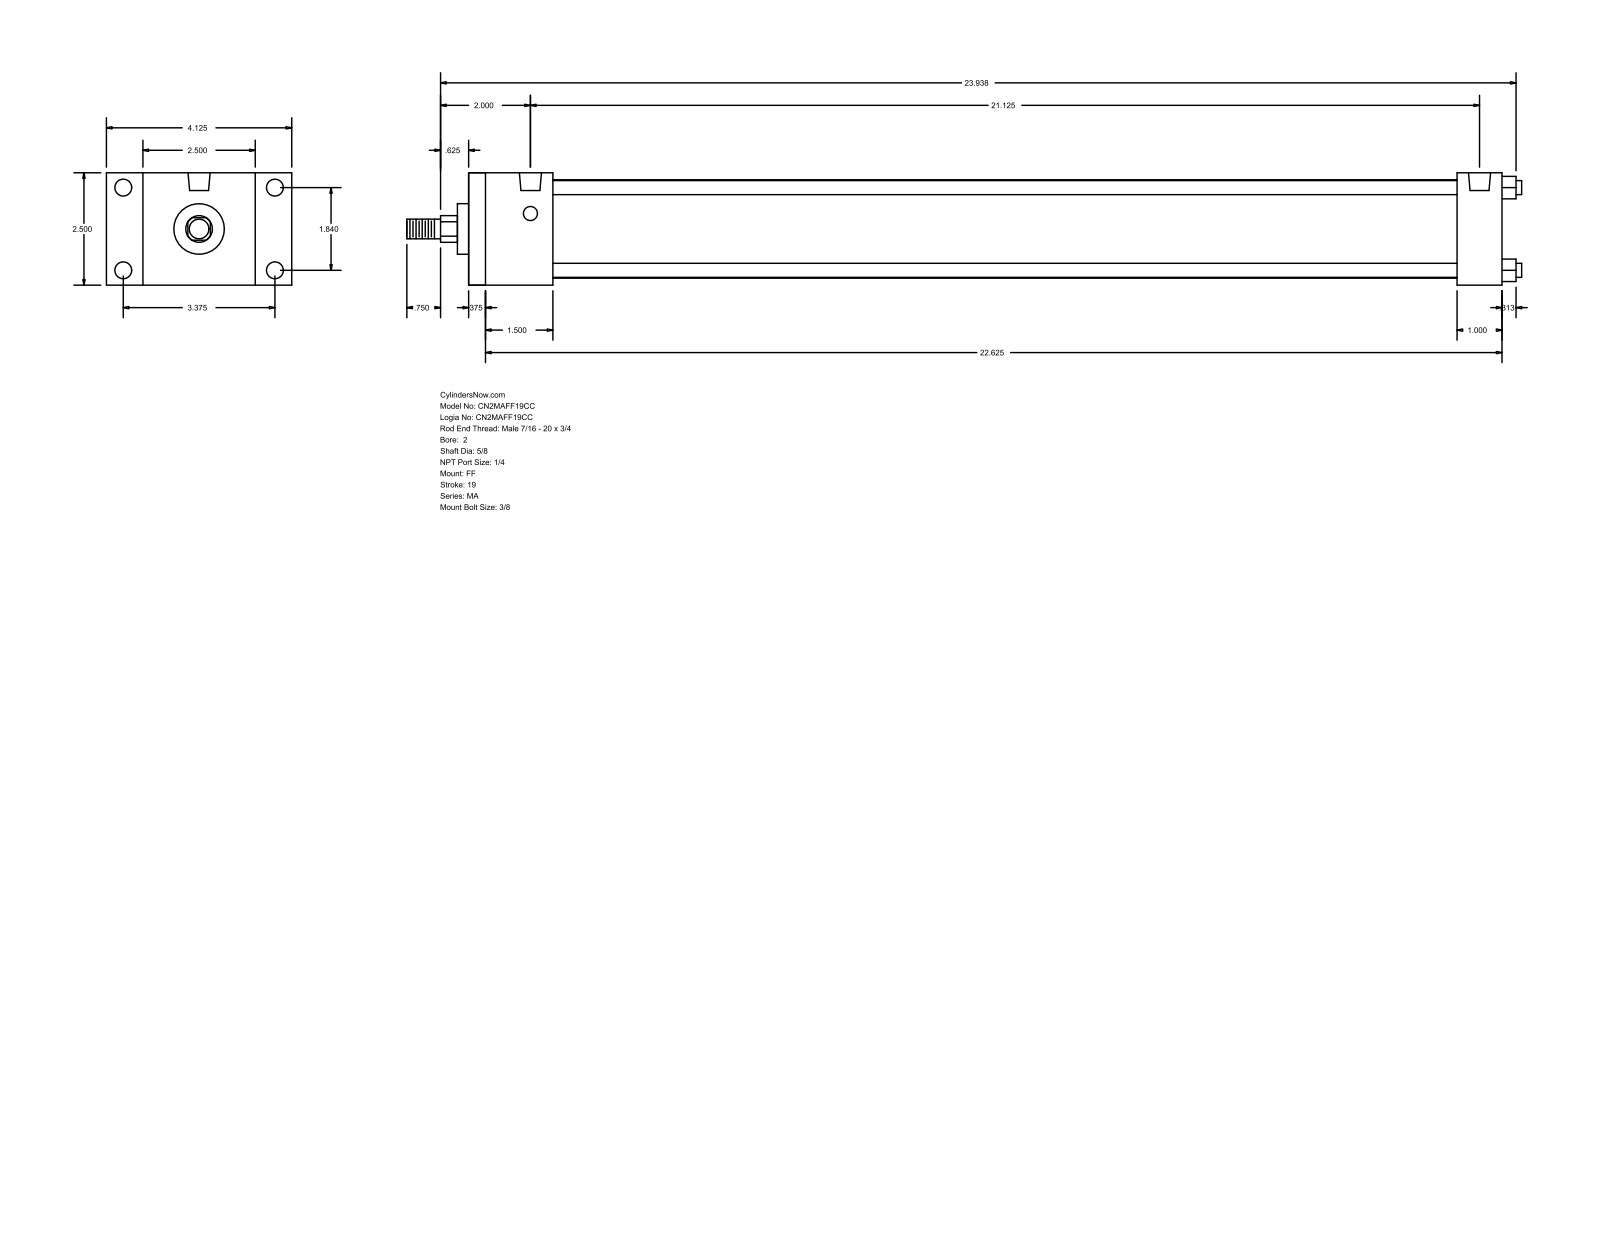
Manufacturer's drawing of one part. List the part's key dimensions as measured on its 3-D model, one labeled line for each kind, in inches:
Part name (STEP PRODUCT): MA_FF__0200_0.625
STEP written by: GSSL Pune (CONFIG_CONTROL_DESIGN)
Units: inches
Bodies: 0 solids, 92 faces (64 planar, 28 cylindrical, 0 other)
Overall size (bounding box): 24.813 × 4.125 × 2.5
Round holes (diameter × count): ⌀0.313 ×4, ⌀0.375 ×4, ⌀0.492 ×2
Round bosses / shafts (diameter × count): ⌀0.313 ×4, ⌀2.19 ×1, ⌀1.125 ×1, ⌀0.625 ×1, ⌀0.437 ×1
Partial cylindrical surfaces — rounded edges, fillets, slot ends (radius × count): R0.297 ×1
Main face-to-face distances: 2.5, 23, 0.375, 22.625, 1.5, 1.875, 22, 21.625, 20.125, 21.125
Hole centre spacings: 1.84, 3.375, 3.844, 21.125
